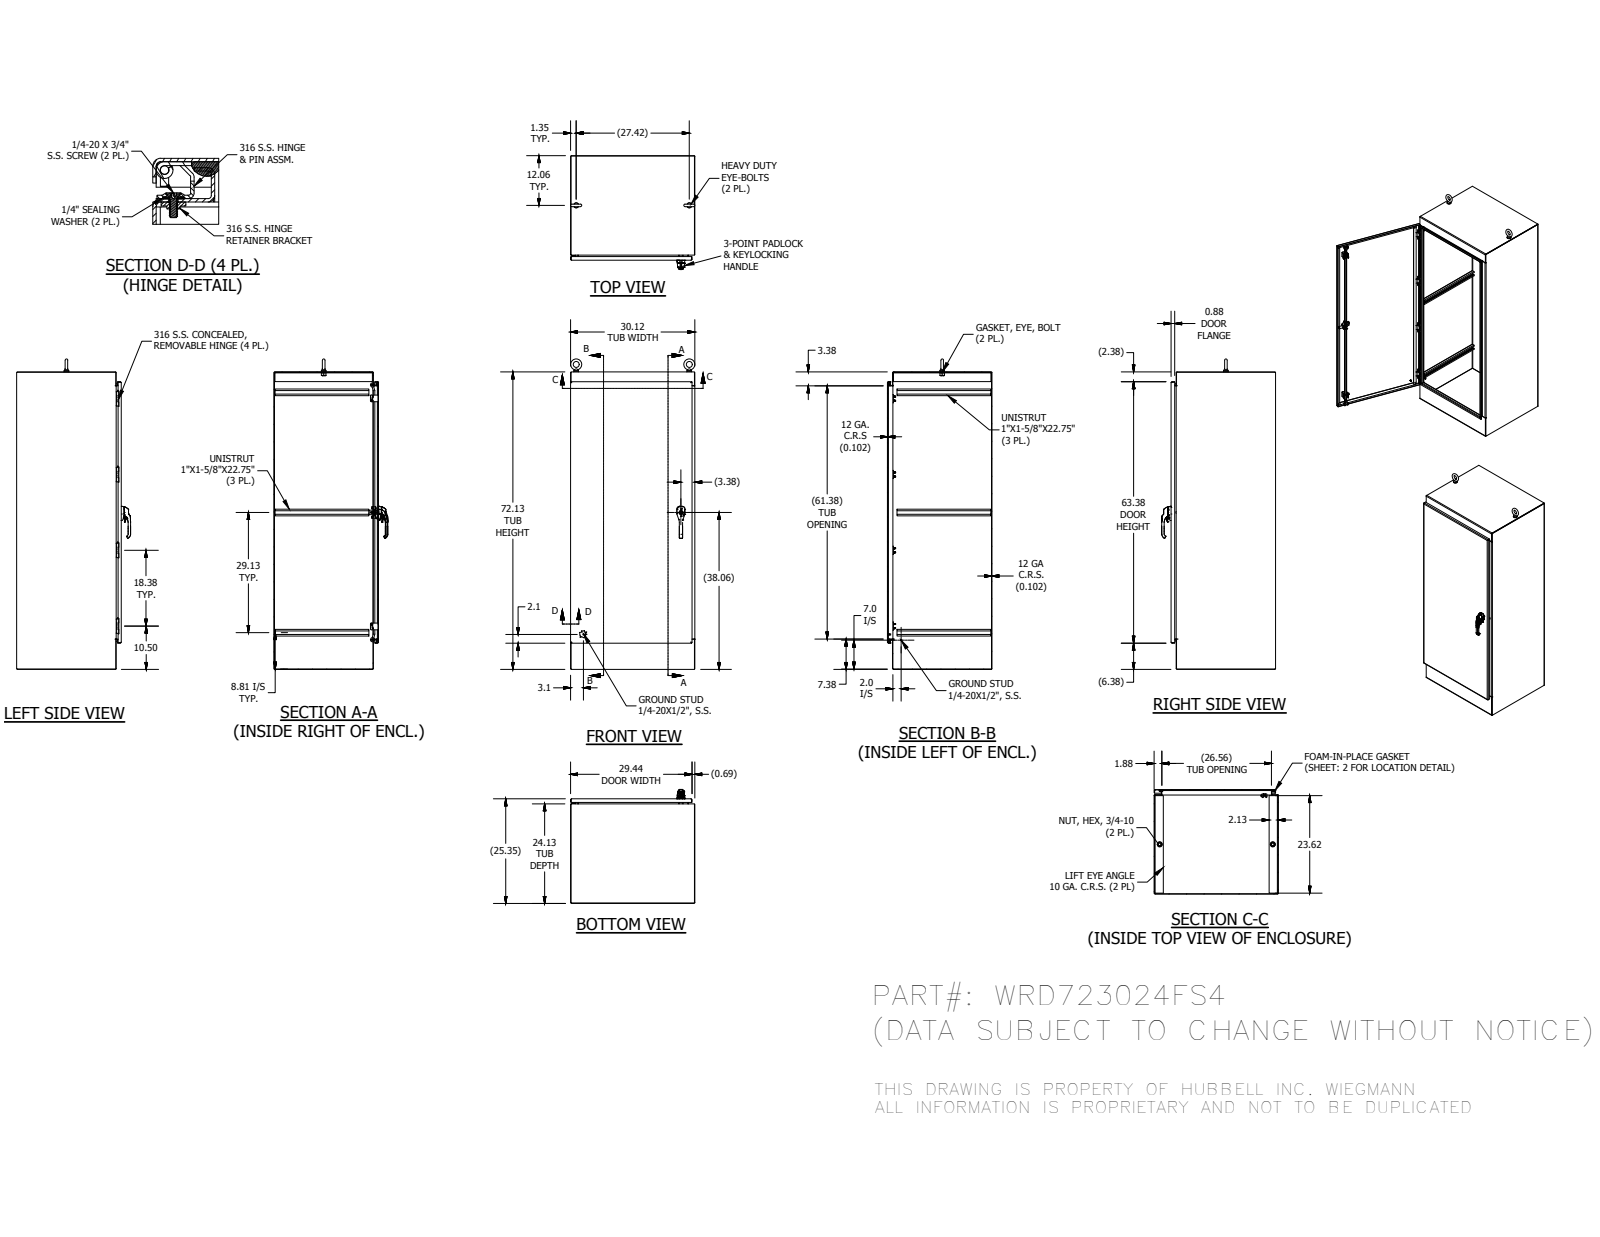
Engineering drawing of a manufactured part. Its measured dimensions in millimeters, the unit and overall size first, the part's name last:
Units: millimetres
Overall size (bounding box): 1911.29 × 765.23 × 701.44
Round holes (diameter × count): ⌀5.84 ×8, ⌀7.02 ×8, ⌀7.14 ×8, ⌀16.51 ×8, ⌀5.08 ×4, ⌀5.4 ×3, ⌀6 ×3, ⌀7.11 ×3, ⌀6.13 ×2, ⌀6.35 ×2, ⌀6.41 ×2, ⌀10.16 ×2
Round bosses / shafts (diameter × count): ⌀6.35 ×15, ⌀15.88 ×8, ⌀10.25 ×8, ⌀4.63 ×8, ⌀31.75 ×2, ⌀28.45 ×2, ⌀25.4 ×2, ⌀19.05 ×2
Partial cylindrical surfaces — rounded edges, fillets, slot ends (radius × count): R0.5 ×164, R0.3 ×85, R1.59 ×27, R0.25 ×24, R3.17 ×20, R0.47 ×19, R2 ×15, R1.27 ×14
Main face-to-face distances: 2.59, 641.23, 762.59, 638.64, 760, 643.82, 765.18, 1829.39, 610.19, 31.04
Hole centre spacings: 12.5, 25.4, 466.73, 933.45, 6.5, 22.5, 51.5, 6
Volume: 19 140 000 mm³ · Surface area: 14 410 000 mm²
Bodies: 85 solids, 3586 faces (1457 planar, 1207 cylindrical, 922 other)
Part name (STEP PRODUCT): WRD723024FS4BLR; WRD3024FS4TOP; WRD3024FS4BTM; WRD7230FS4DR (+8 more)
STEP written by: Autodesk Inventor 2016 (AUTOMOTIVE_DESIGN)
